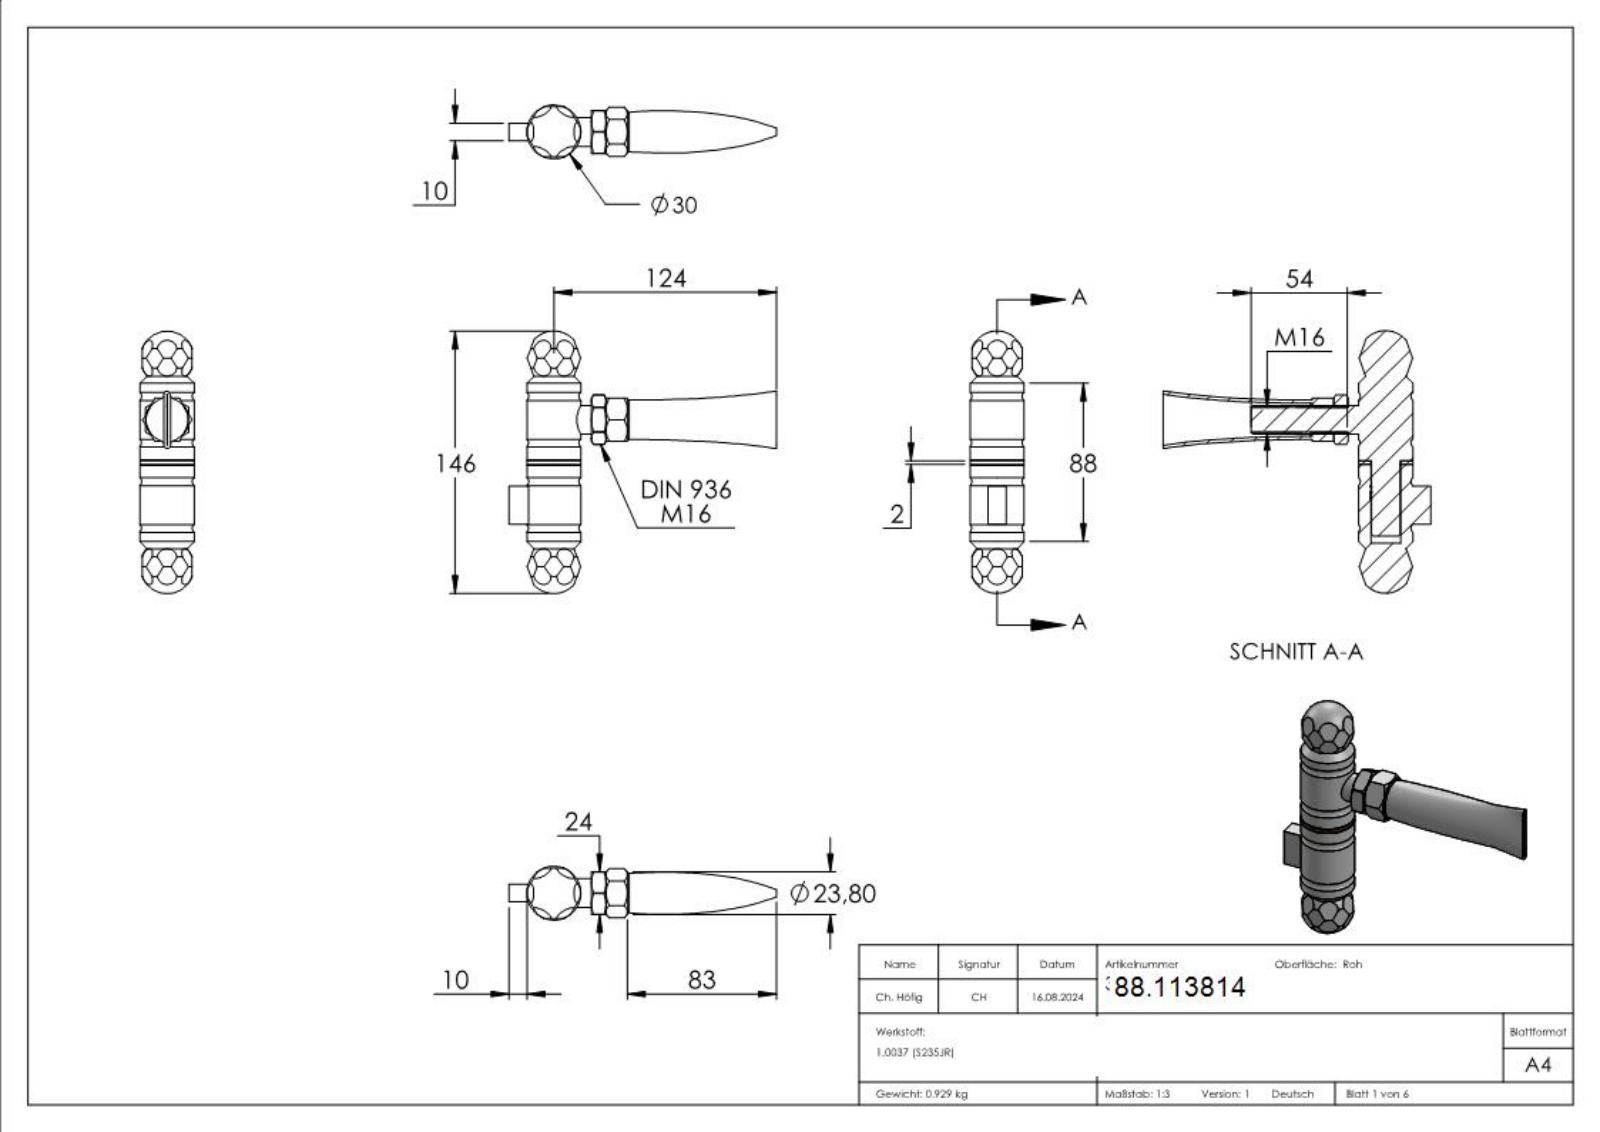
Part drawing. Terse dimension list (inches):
name: 3814; 3814 Teil1-4_3814 Teil2; 3814 Teil1-4_3814 Teil3; DIN 936 M8-M24_DIN 936 M16 (+2 more)
written by: SolidWorks 2018 (CONFIG_CONTROL_DESIGN)
unit: in
bodies: 5 solids, 372 faces (164 planar, 38 cylindrical, 170 other)
size: 5.866 × 5.748 × 1.181
volume: 7.246 in³; area: 60.31 in²
holes: 1× ⌀0.551, 1× ⌀0.65, 1× ⌀0.669
bosses: 2× ⌀0.63, 1× ⌀1.181
rounds: 6× R0.02, 1× R0.329
face distances: 1.099, 1.562, 0.079, 1.811, 0.463, 2.661, 1.098, 2.126, 0.352, 0.746
